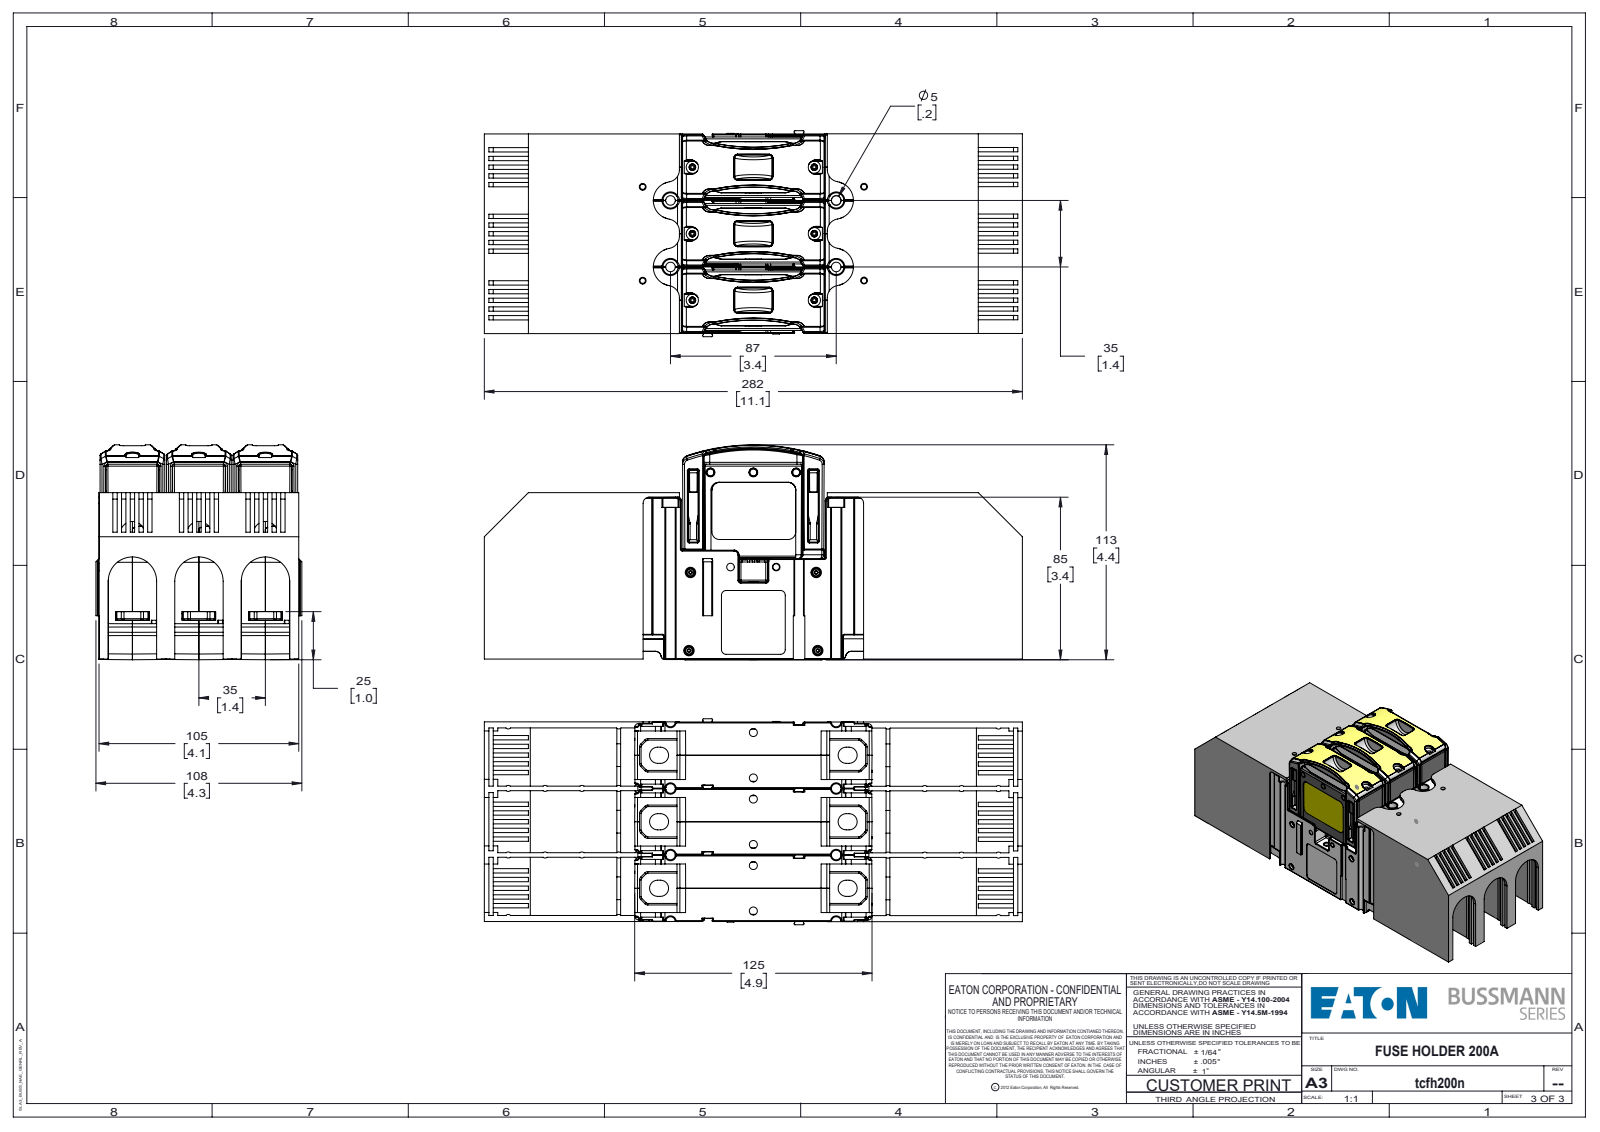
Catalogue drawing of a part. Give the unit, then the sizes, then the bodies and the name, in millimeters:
Units: millimetres
Overall size (bounding box): 124.6 × 85.3 × 38.3
Round holes (diameter × count): ⌀2.2 ×12, ⌀1.4 ×4, ⌀2.1 ×4, ⌀2.79 ×4, ⌀3 ×4, ⌀4.5 ×4, ⌀4 ×2, ⌀4.2 ×2, ⌀4.6 ×2, ⌀16 ×1
Round bosses / shafts (diameter × count): ⌀2.2 ×20, ⌀5.7 ×4, ⌀3.6 ×4, ⌀2 ×4, ⌀7 ×2, ⌀3 ×2
Partial cylindrical surfaces — rounded edges, fillets, slot ends (radius × count): R0.5 ×180, R1 ×77, R1.5 ×60, R0.2 ×38, R0.8 ×32, R2 ×32, R0.15 ×24, R0.8 ×24
Main face-to-face distances: 34.89, 1.2, 0.51, 32.6, 29.91, 0.7, 4.69, 2, 30.2, 1.71
Hole centre spacings: 20.22, 39.45, 41.97, 77.28, 0.64, 58.12, 62.19, 12.5
Volume: 104 443 mm³ · Surface area: 112 844 mm²
Bodies: 20 solids, 2910 faces (1571 planar, 961 cylindrical, 378 other)
Part name (STEP PRODUCT): 2A2957-1; 2A3085-X_2A3085-2 200; TCFH200N; 2A3450 (+7 more)
STEP written by: SolidWorks 2016 (CONFIG_CONTROL_DESIGN)
